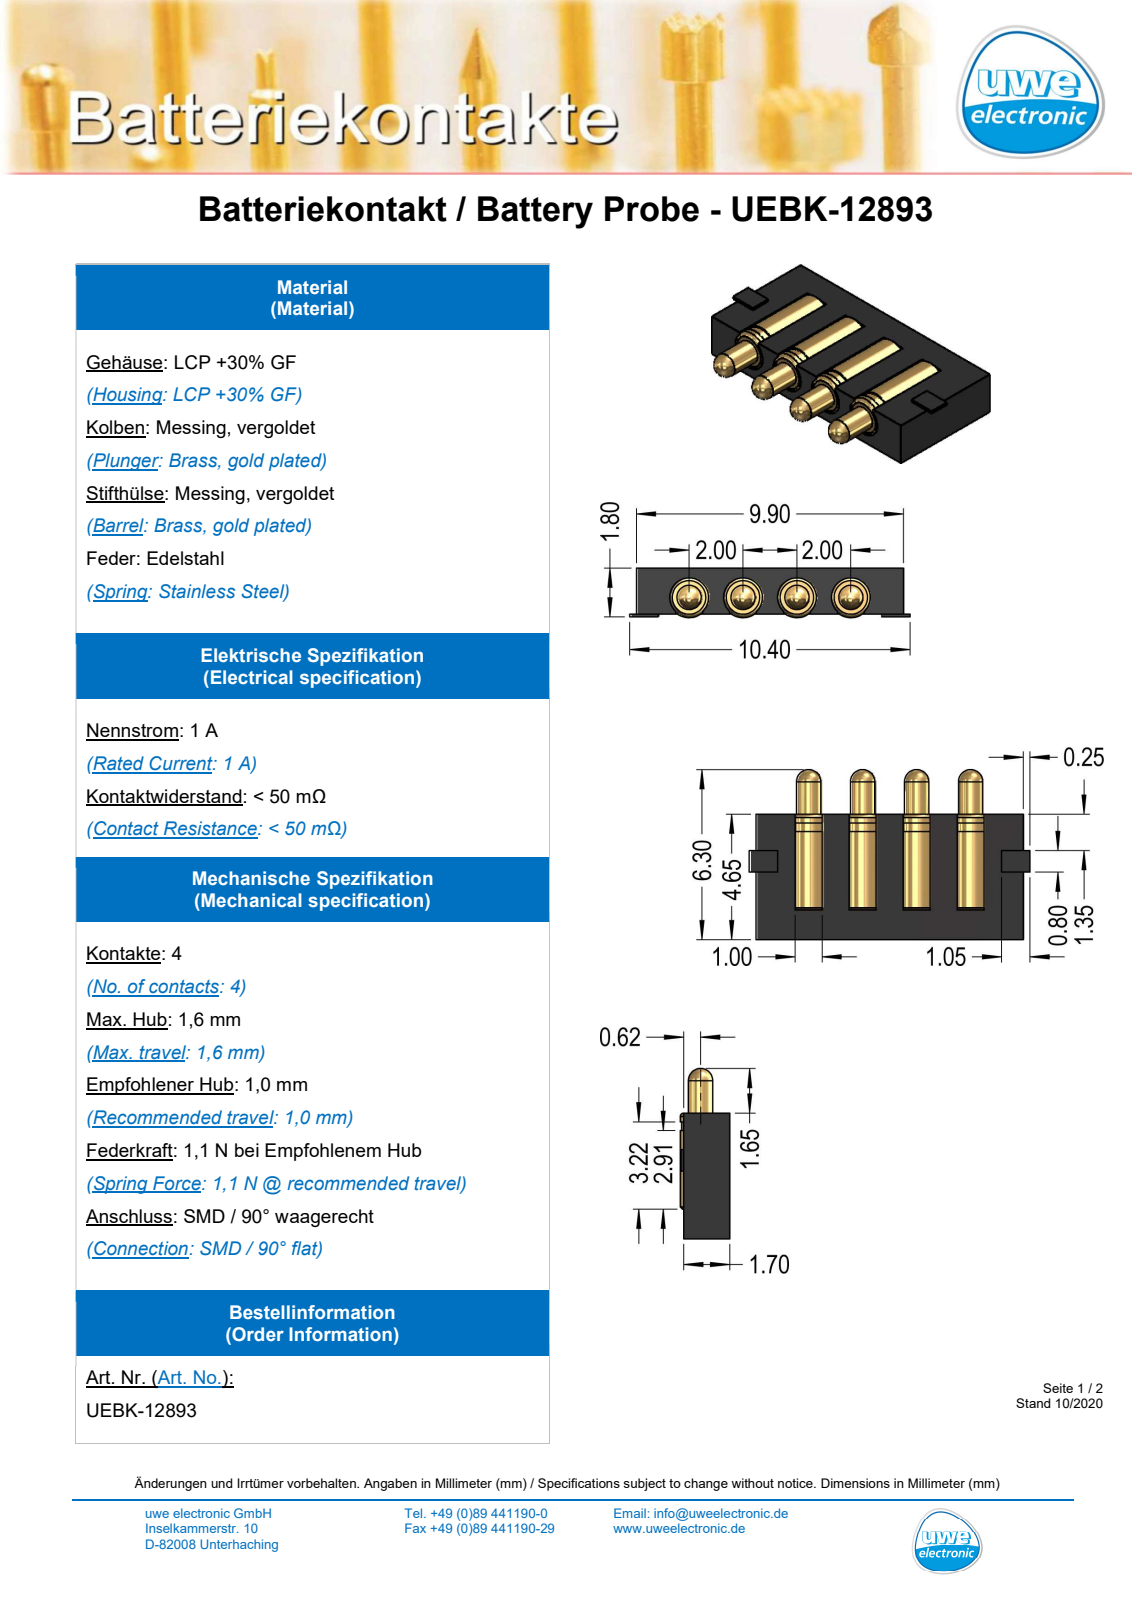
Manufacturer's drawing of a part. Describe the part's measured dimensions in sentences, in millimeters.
The part is named "UEBK-12893-Pin; UEBK-12893-Gehäuse; UEBK-12893". Its 3-D file was written by "SolidWorks 2020 (AUTOMOTIVE_DESIGN)". It is 5 solids with 110 faces: 46 planar, 40 cylindrical and 24 other. Overall it measures 10.4 by 6.3 by 1.83 millimeters. Its volume is 84 cubic millimeters and its surface area 277 square millimeters. Round bosses or shafts: 4 of diameter 1.5, 4 of diameter 1.4, 4 of diameter 0.9. Partial cylindrical surfaces (rounded edges, fillets, slot ends): 4 of radius 0.72. The main face-to-face distances are 1.7, 4.65, 1.1, 3.55, 9.9, 1, 2, 3, 1.8, 4.
